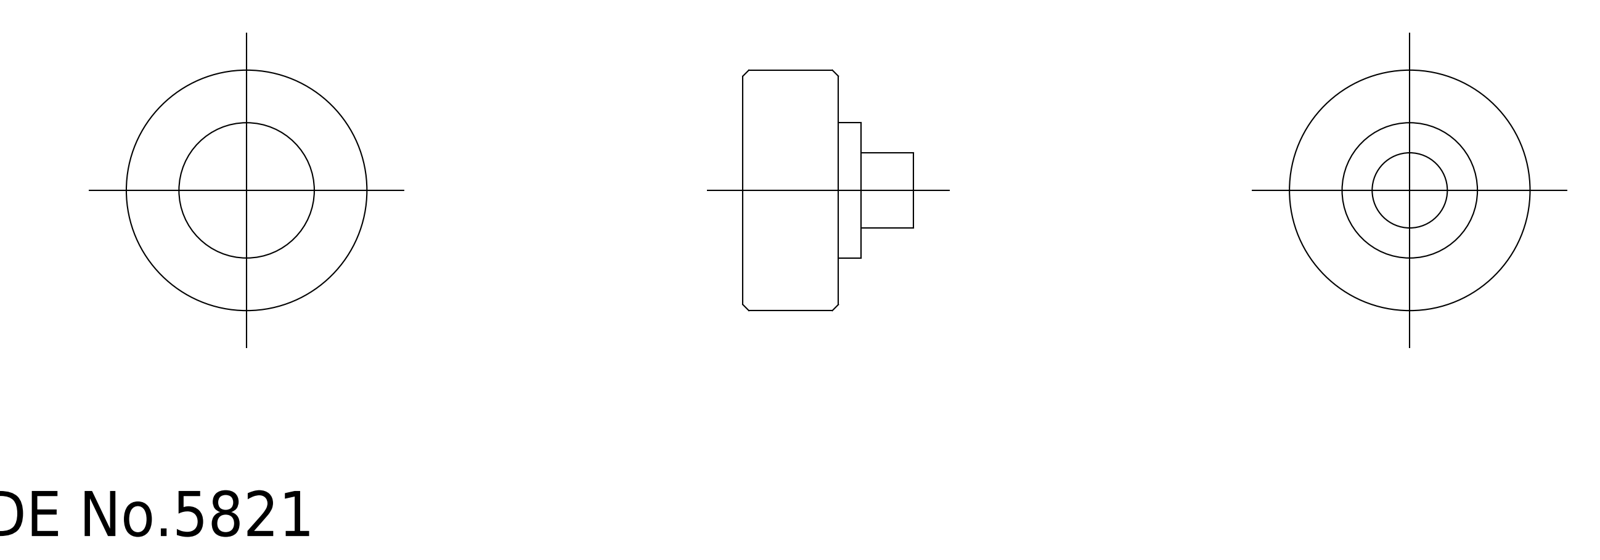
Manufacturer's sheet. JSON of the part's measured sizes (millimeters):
{"part_name": "roller", "step_written_by": "CADfix (AUTOMOTIVE_DESIGN)", "units": "millimeters", "bodies": {"solids": 1, "faces": 28, "planar": 0, "cylindrical": 0, "other": 28}, "overall_size": [16, 16, 11.35], "volume_mm3": 1424, "surface_area_mm2": 1215}
